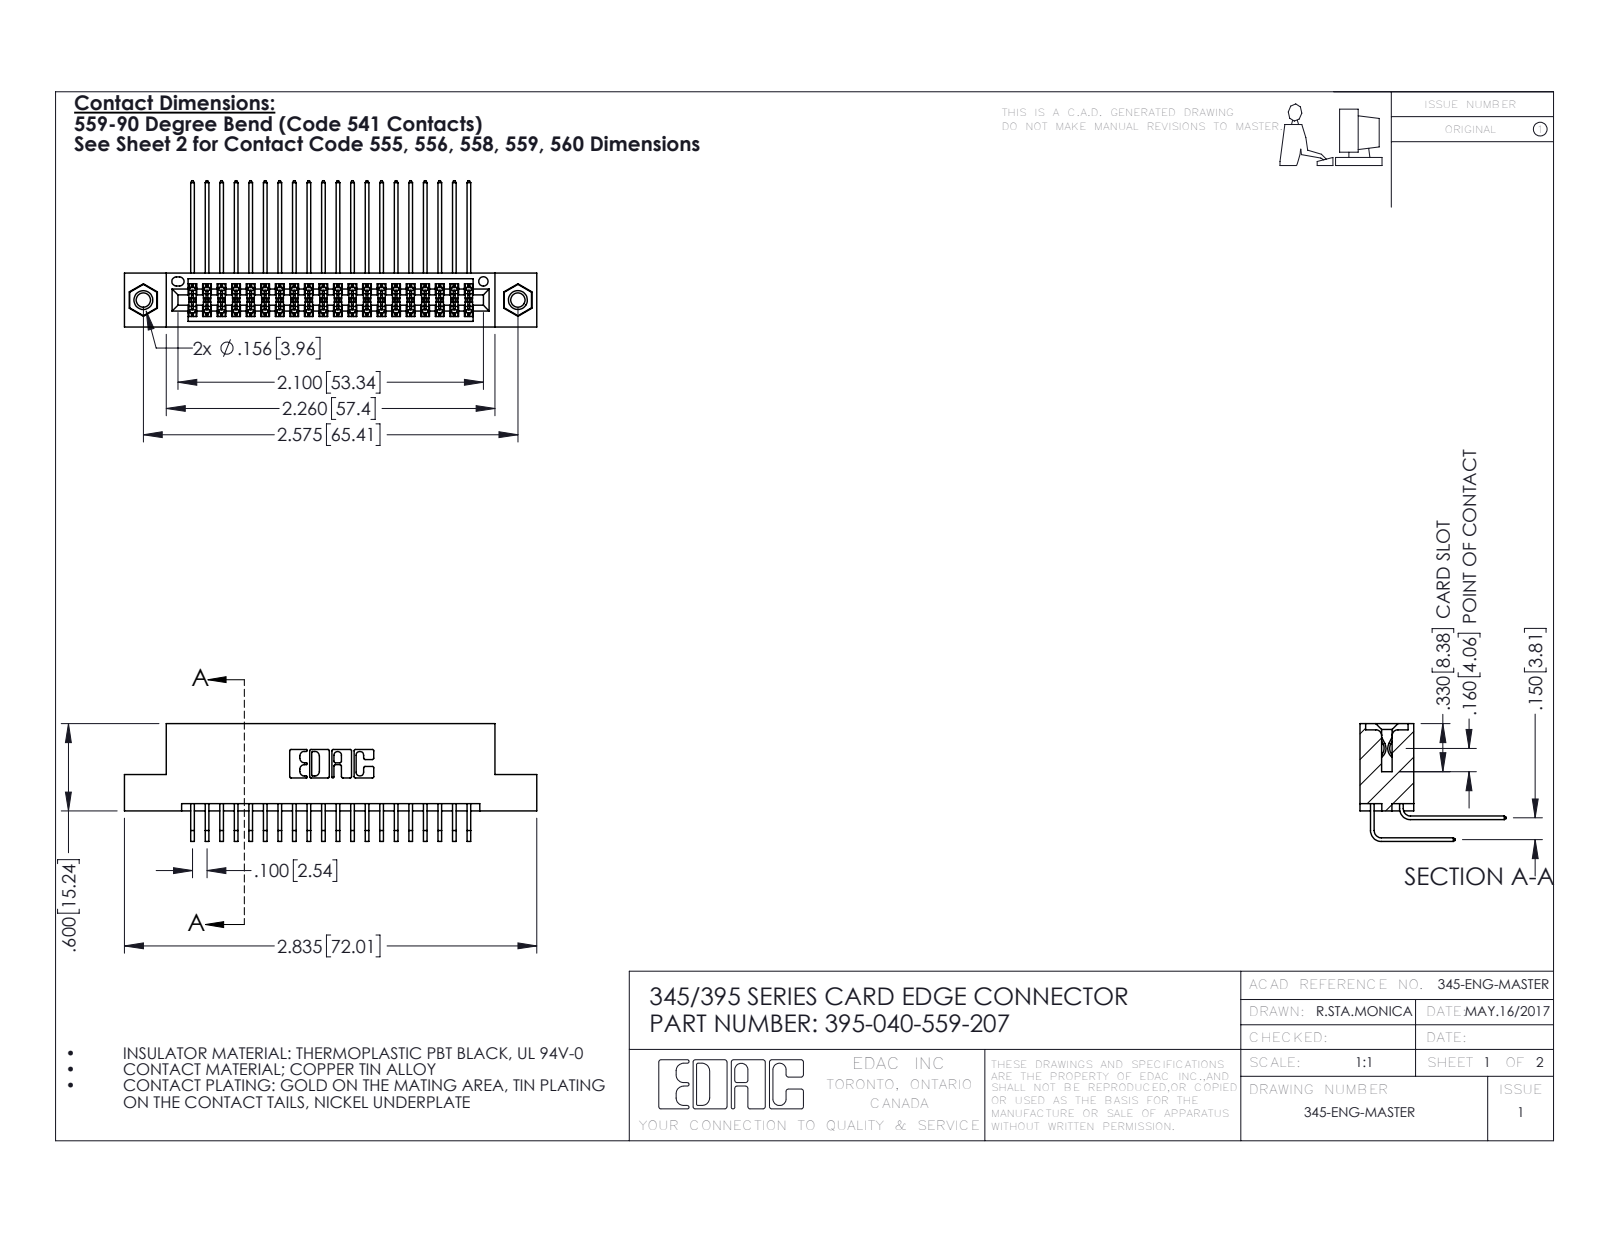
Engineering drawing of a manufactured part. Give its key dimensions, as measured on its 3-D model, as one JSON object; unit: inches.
{"part_name": "345 Part_Flush Mounting Lugs - 0.156 Dia-TI; 345-292-001_558 559 Tail - 1; 345-292-001_559 Tail - 2; 395-040-559-207 (+1 more)", "step_written_by": "SolidWorks 2016 (CONFIG_CONTROL_DESIGN)", "units": "inches", "bodies": {"solids": 43, "faces": 2266, "planar": 1512, "cylindrical": 738, "other": 16}, "overall_size": [2.835, 1.005, 0.809], "volume_in3": 0.428, "surface_area_in2": 17.12, "round_holes": [[0.098, 2], [0.125, 2], [0.156, 2], [0.064, 1]], "round_bosses_or_shafts": [[0.155, 2]], "partial_cylinders_radius": [[0.006, 61], [0.01, 22], [0.007, 6], [0.031, 6], [0.026, 3], [0.014, 2], [0.019, 2], [0.022, 2]], "face_to_face_distances": [0.072, 0.298, 0.2, 0.37, 0.098, 0.272, 0.025, 0.225, 0.15, 0.175], "hole_center_spacings": [0.27, 2.341, 2.575]}
